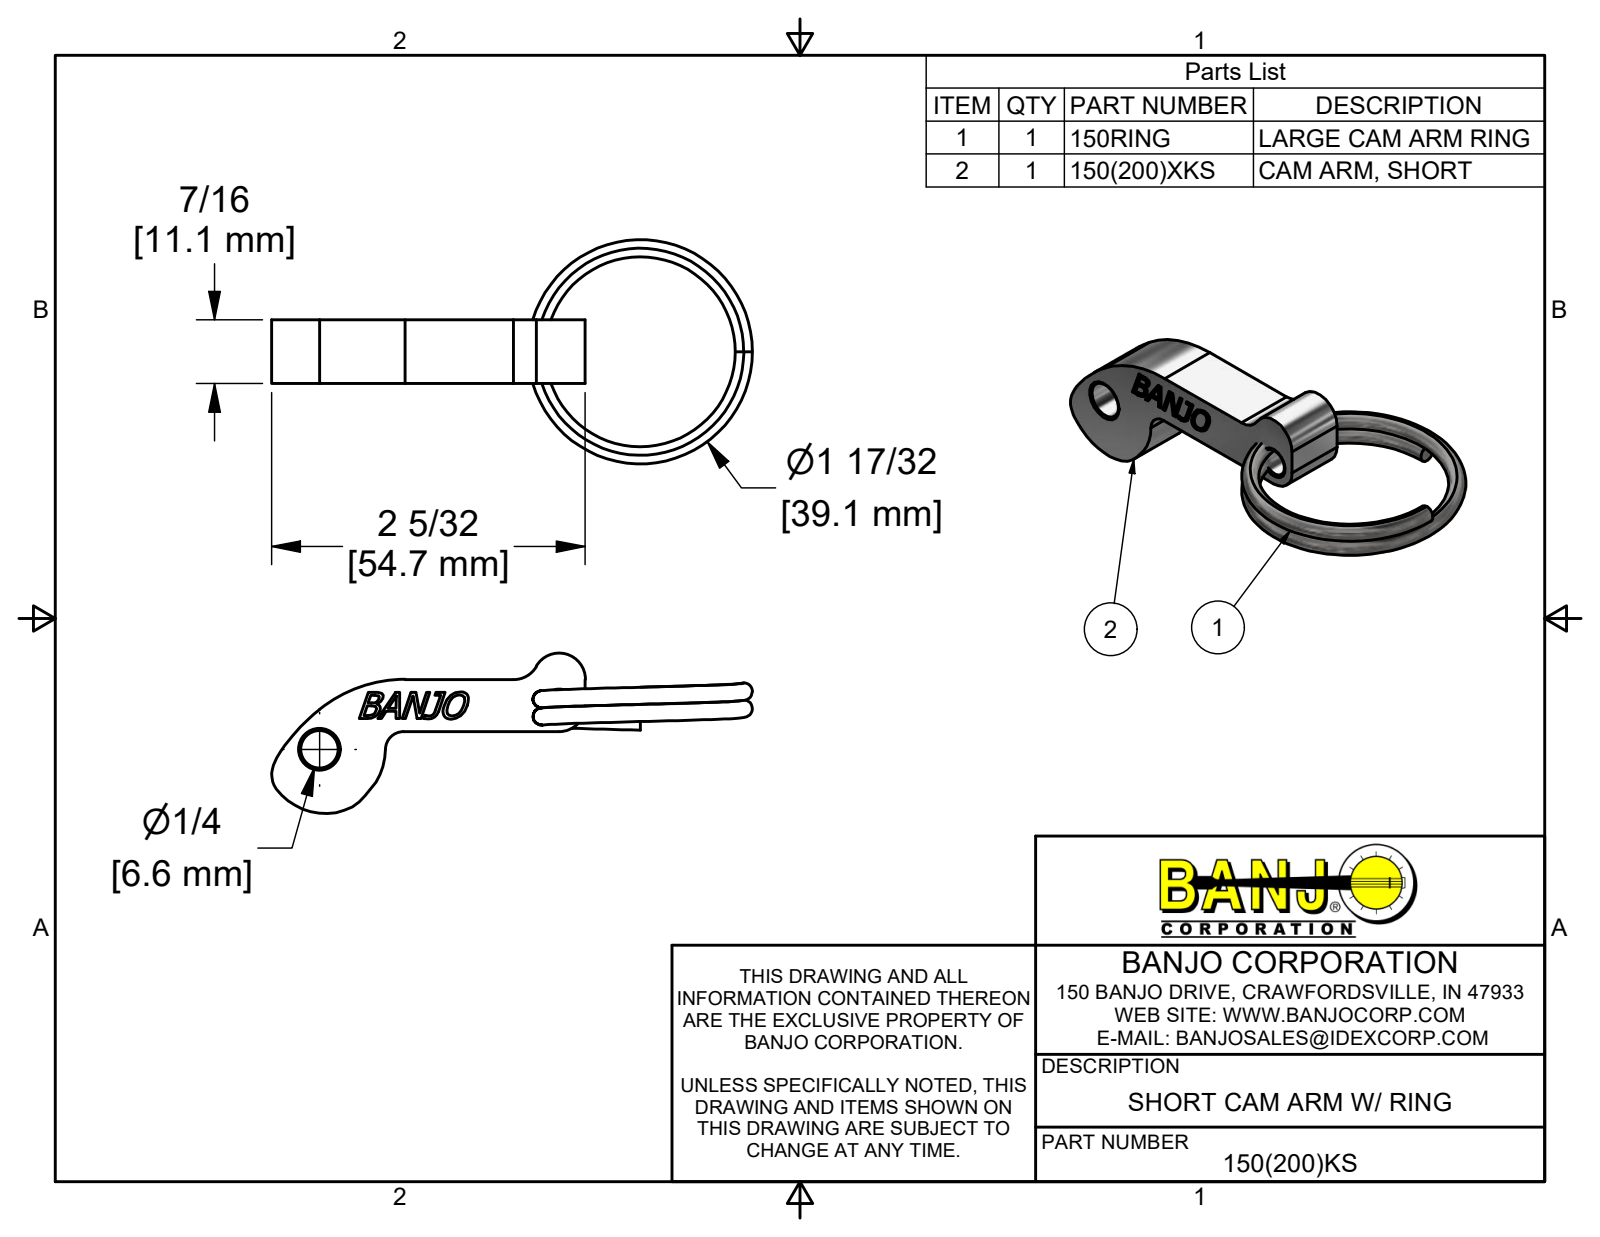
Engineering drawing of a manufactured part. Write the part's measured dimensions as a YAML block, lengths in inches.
part_name: "150(200)KS; 150(200)XKS; 150RING"
step_written_by: "Autodesk Inventor 2018 (AUTOMOTIVE_DESIGN)"
units: inches
bodies: {solids: 2, faces: 187, planar: 104, cylindrical: 8, other: 75}
overall_size: [3.287, 1.541, 1.096]
volume: 0.468
surface_area: 8.2
round_holes:
  - {diameter: 0.258, count: 1}
partial_cylinders:
  - {radius: 0.18, count: 3}
  - {radius: 0.075, count: 2}
  - {radius: 0.124, count: 1}
  - {radius: 0.94, count: 1}
face_to_face_distances: [0.438, 0.358, 0.103, 0.253, 0.15, 0.255, 0.105, 0.02, 0.418, 0.398]
